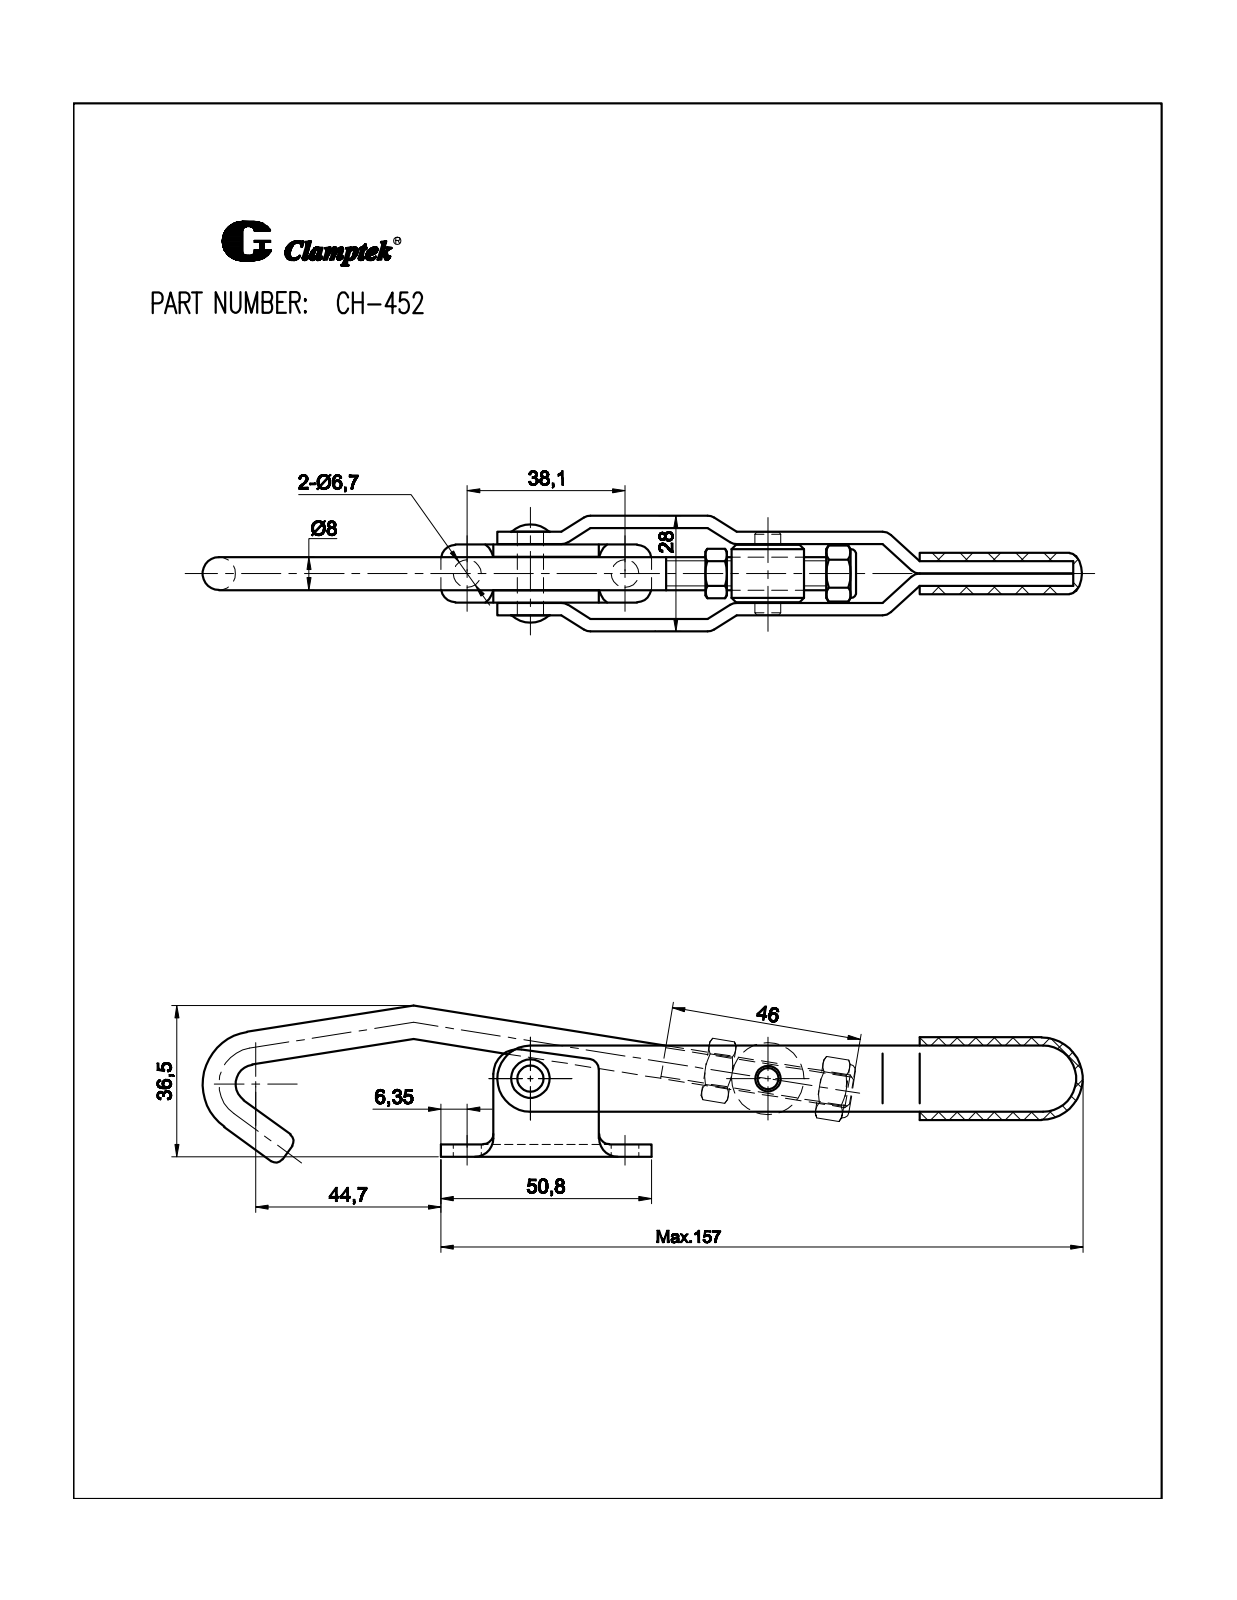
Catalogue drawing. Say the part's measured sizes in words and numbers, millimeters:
The part is named "CH-452; M8防松_默认". Its 3-D file was written by "SolidWorks 2008 (CONFIG_CONTROL_DESIGN)". It is 8 solids with 604 faces: 218 planar, 170 cylindrical and 216 other. Overall it measures 212.92 by 37.75 by 26.8 millimeters. Its volume is 34 422 cubic millimeters and its surface area 24 010 square millimeters. Round holes: 2 of diameter 6.4, 2 of diameter 6.5, 2 of diameter 6.7, 1 of diameter 0.93, 1 of diameter 5.8, 1 of diameter 8. Round bosses or shafts: 4 of diameter 8, 1 of diameter 17.4, 1 of diameter 11, 1 of diameter 9.5, 1 of diameter 0.83. Partial cylindrical surfaces (rounded edges, fillets, slot ends): 16 of radius 3, 4 of radius 1.5, 2 of radius 8, 1 of radius 2.5, 1 of radius 6, 1 of radius 9.5. The main face-to-face distances are 3, 3.3, 20.5, 6.3, 17.5, 17.2, 14.2, 3.1, 2.6, 5.6. The hole center spacings are 9.94, 38.1, 57.29, 63.
